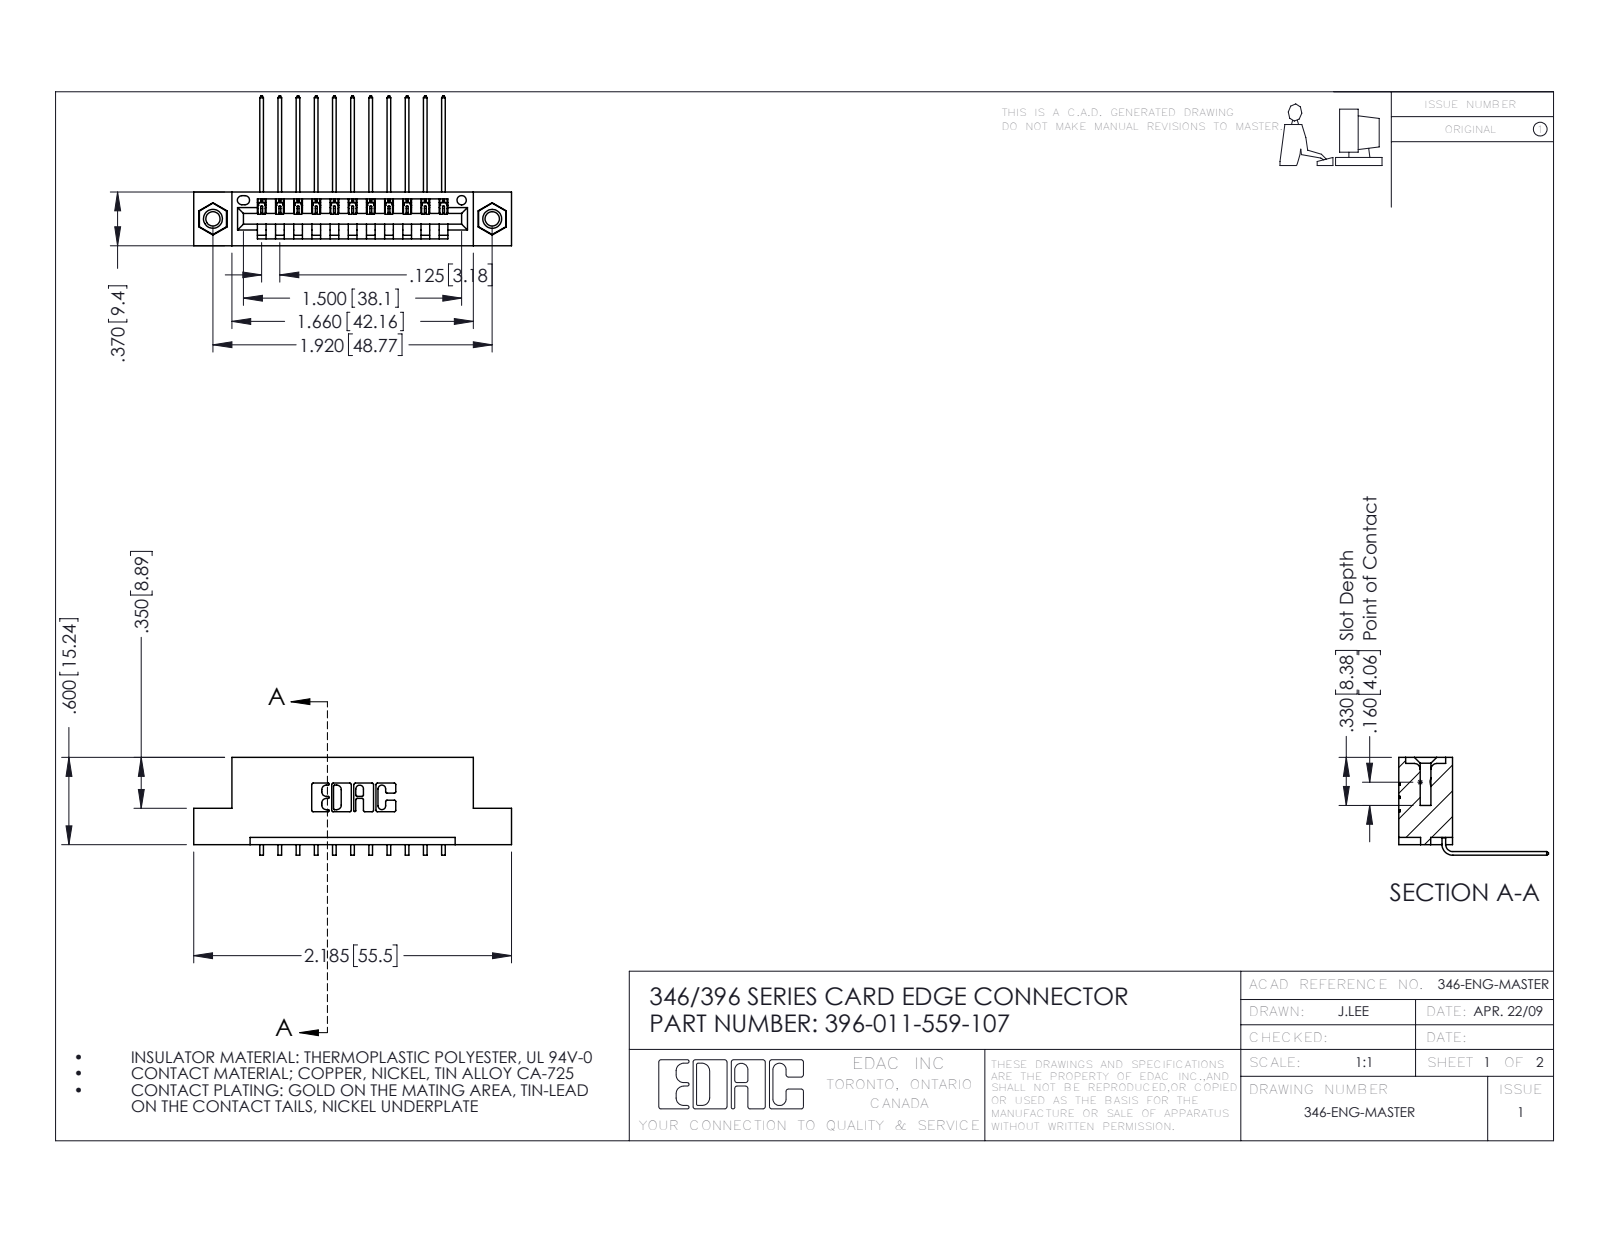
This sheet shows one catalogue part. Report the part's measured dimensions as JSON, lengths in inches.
{"part_name": "345-250-001_345-250-005-103; 346 Part_Flush Mounting Lugs - 0.156 Dia-TI; 396-011-559-107; 345-292-001_558 559 Tail - 1", "step_written_by": "SolidWorks 2016 (CONFIG_CONTROL_DESIGN)", "units": "inches", "bodies": {"solids": 14, "faces": 842, "planar": 570, "cylindrical": 256, "other": 16}, "overall_size": [2.185, 1.03, 0.673], "volume_in3": 0.313, "surface_area_in2": 9.797, "round_holes": [[0.098, 2], [0.125, 2], [0.156, 2], [0.064, 1]], "round_bosses_or_shafts": [[0.155, 2]], "partial_cylinders_radius": [[0.006, 22], [0.01, 22], [0.007, 6], [0.031, 6], [0.026, 3], [0.031, 2], [0.04, 2], [0.014, 1]], "face_to_face_distances": [0.25, 0.048, 0.322, 0.37, 0.072, 0.025, 0.298, 0.148, 0.222, 0.1], "hole_center_spacings": [0.246, 1.715, 1.92]}
